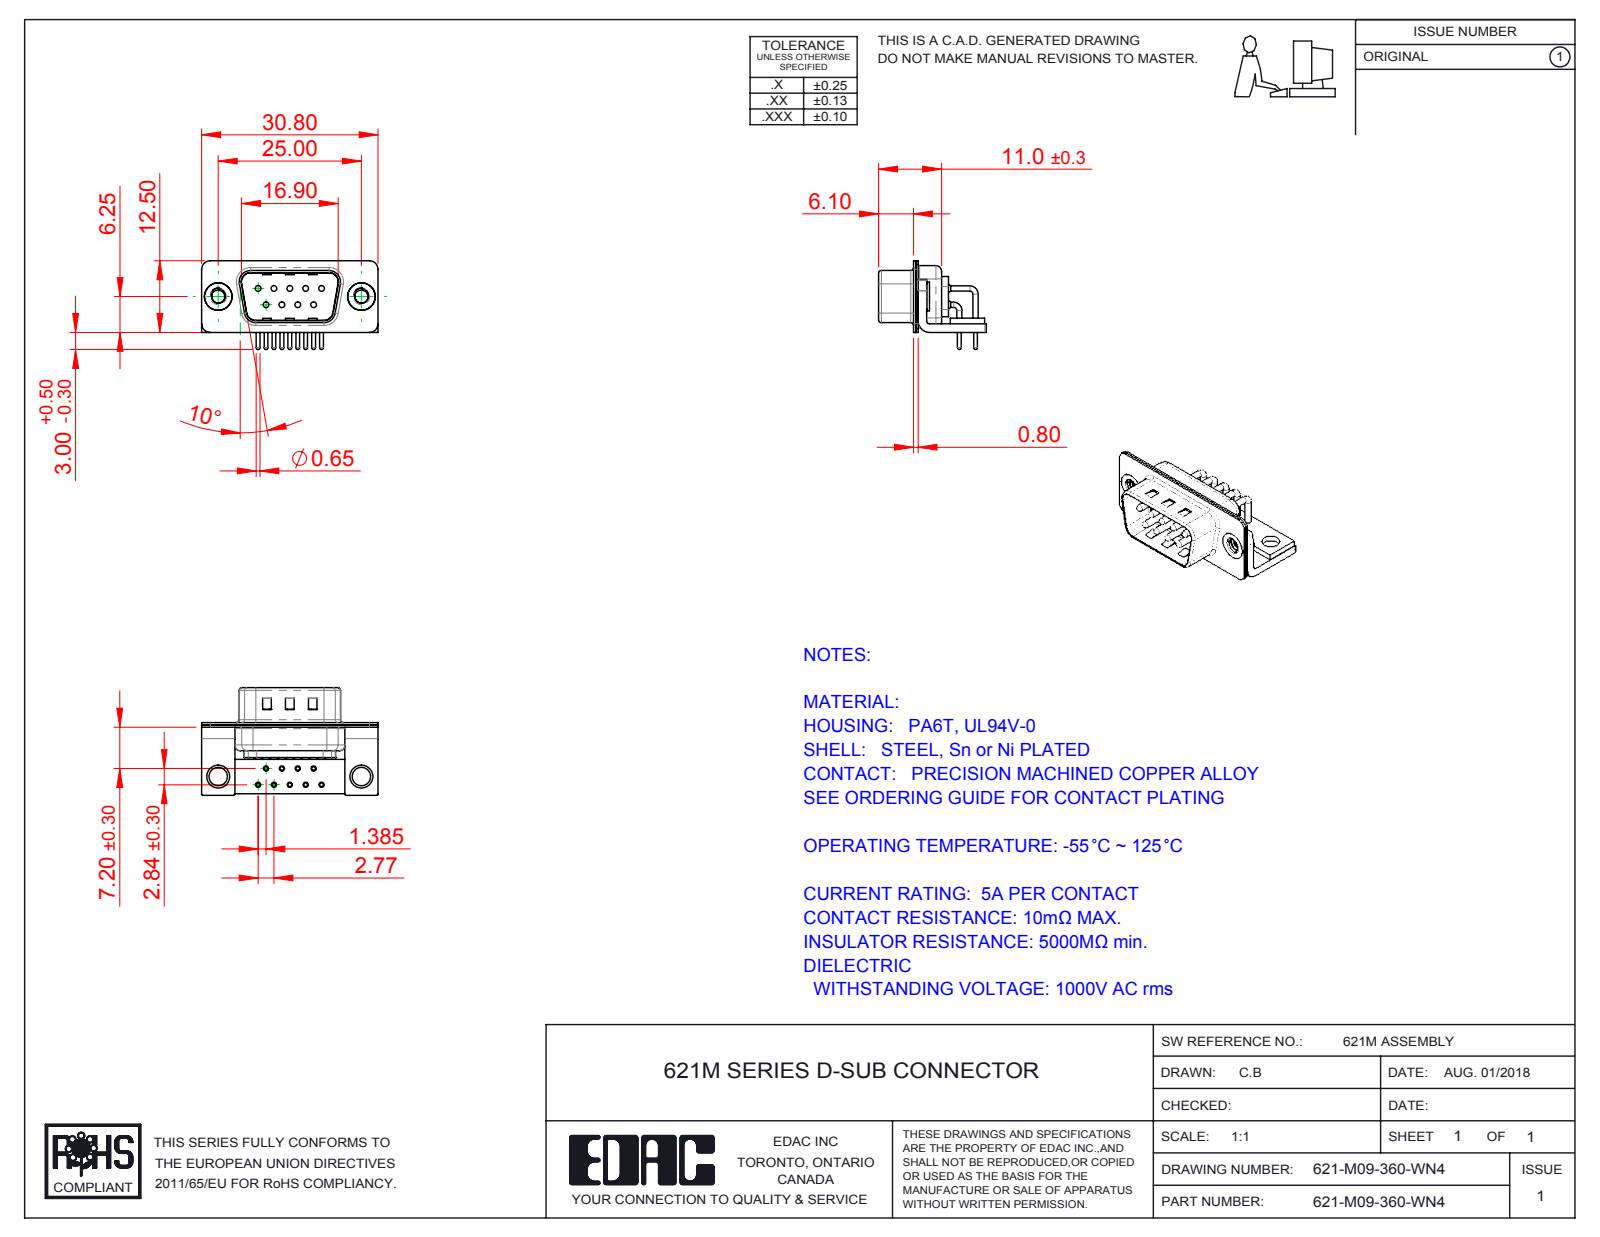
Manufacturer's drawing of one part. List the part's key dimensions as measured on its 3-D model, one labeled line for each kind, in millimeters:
Part name (STEP PRODUCT): 621M Contact Row 1; 621M Shell Front_09 Contacts; 621M Shell Rear_09 Contacts; 621M Housing_09 Contacts (+5 more)
STEP written by: SolidWorks 2016 (CONFIG_CONTROL_DESIGN)
Units: millimetres
Bodies: 17 solids, 1362 faces (709 planar, 493 cylindrical, 160 other)
Overall size (bounding box): 30.8 × 18.8 × 15.49
Volume: 1 755 mm³ · Surface area: 4 812 mm²
Round holes (diameter × count): ⌀0.9 ×9, ⌀1 ×9, ⌀1.7 ×9, ⌀2 ×9, ⌀2.26 ×2, ⌀3.2 ×2, ⌀4 ×2, ⌀4.8 ×2
Round bosses / shafts (diameter × count): ⌀1.5 ×9, ⌀0.9 ×9, ⌀0.65 ×9, ⌀5 ×2, ⌀4.9 ×2
Partial cylindrical surfaces — rounded edges, fillets, slot ends (radius × count): R0.25 ×16, R1.5 ×16, R2 ×13, R0.5 ×9, R1.01 ×9, R1.6 ×8, R0.6 ×4, R0.65 ×4
Main face-to-face distances: 0.4, 1.5, 0.8, 0.85, 1.25, 1, 10.4, 9.55, 1.9, 2.5
Hole centre spacings: 3.16, 2.77, 5.54, 5.03, 5.04, 8.31, 7.48, 7.49
